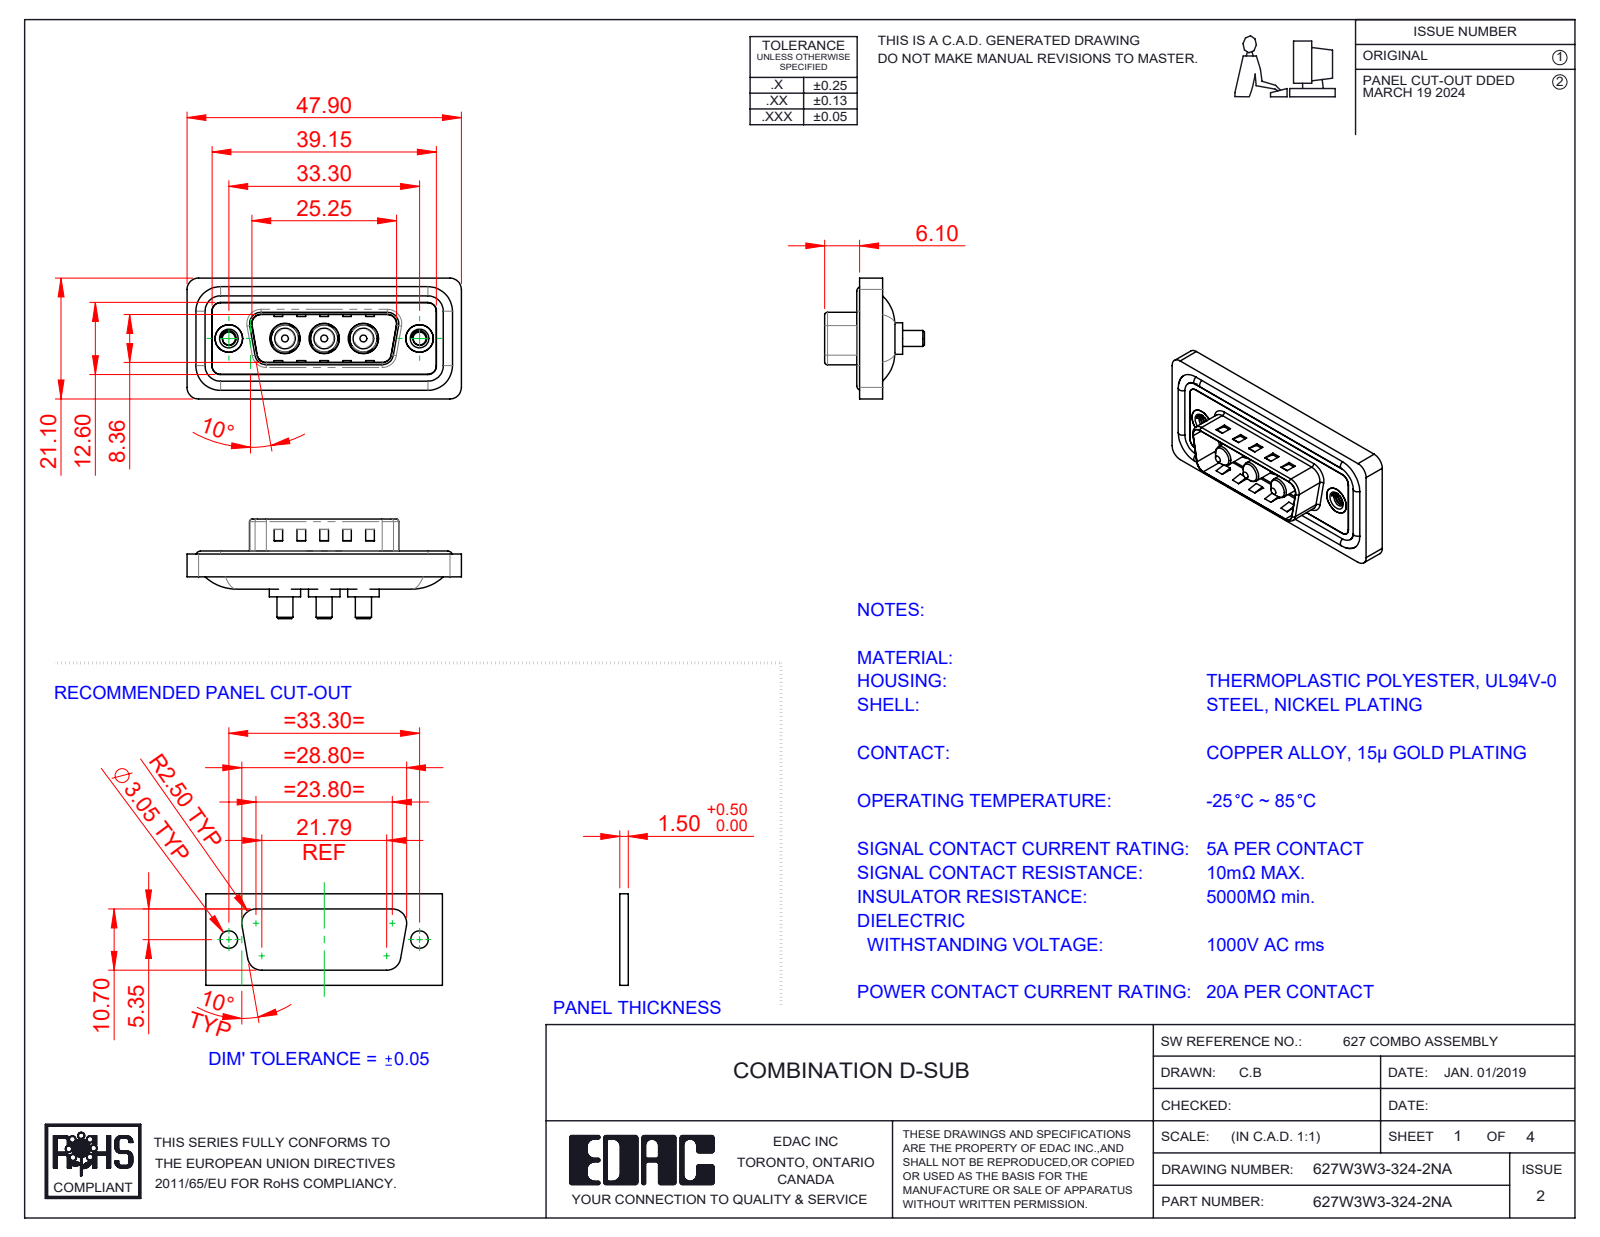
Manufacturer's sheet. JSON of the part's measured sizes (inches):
{"part_name": "Power Pin_20A S; 627Combo Threaded Rivet_A; 627Combo Shell Front_15 Contacts; 627Combo Housing_3W3 (+3 more)", "step_written_by": "SolidWorks 2023 (CONFIG_CONTROL_DESIGN)", "units": "inches", "bodies": {"solids": 13, "faces": 562, "planar": 207, "cylindrical": 243, "other": 112}, "overall_size": [1.886, 0.831, 0.685], "volume_in3": 0.341, "surface_area_in2": 13.56, "round_holes": [[0.191, 3], [0.209, 3], [0.089, 2], [0.157, 2], [0.189, 2], [0.197, 2]], "round_bosses_or_shafts": [[0.063, 4], [0.217, 3], [0.205, 3], [0.187, 3], [0.148, 3], [0.142, 3], [0.11, 3], [0.193, 2]], "partial_cylinders_radius": [[0.059, 26], [0.079, 20], [0.02, 8], [0.063, 8], [0.01, 4], [0.024, 4], [0.026, 4], [0.035, 4]], "face_to_face_distances": [0.016, 0.043, 0.059, 0.02, 0.063, 0.122, 0.114, 0.157, 0.032, 0.377], "hole_center_spacings": [0.27, 0.386, 0.656, 0.925, 0.539, 1.311]}
